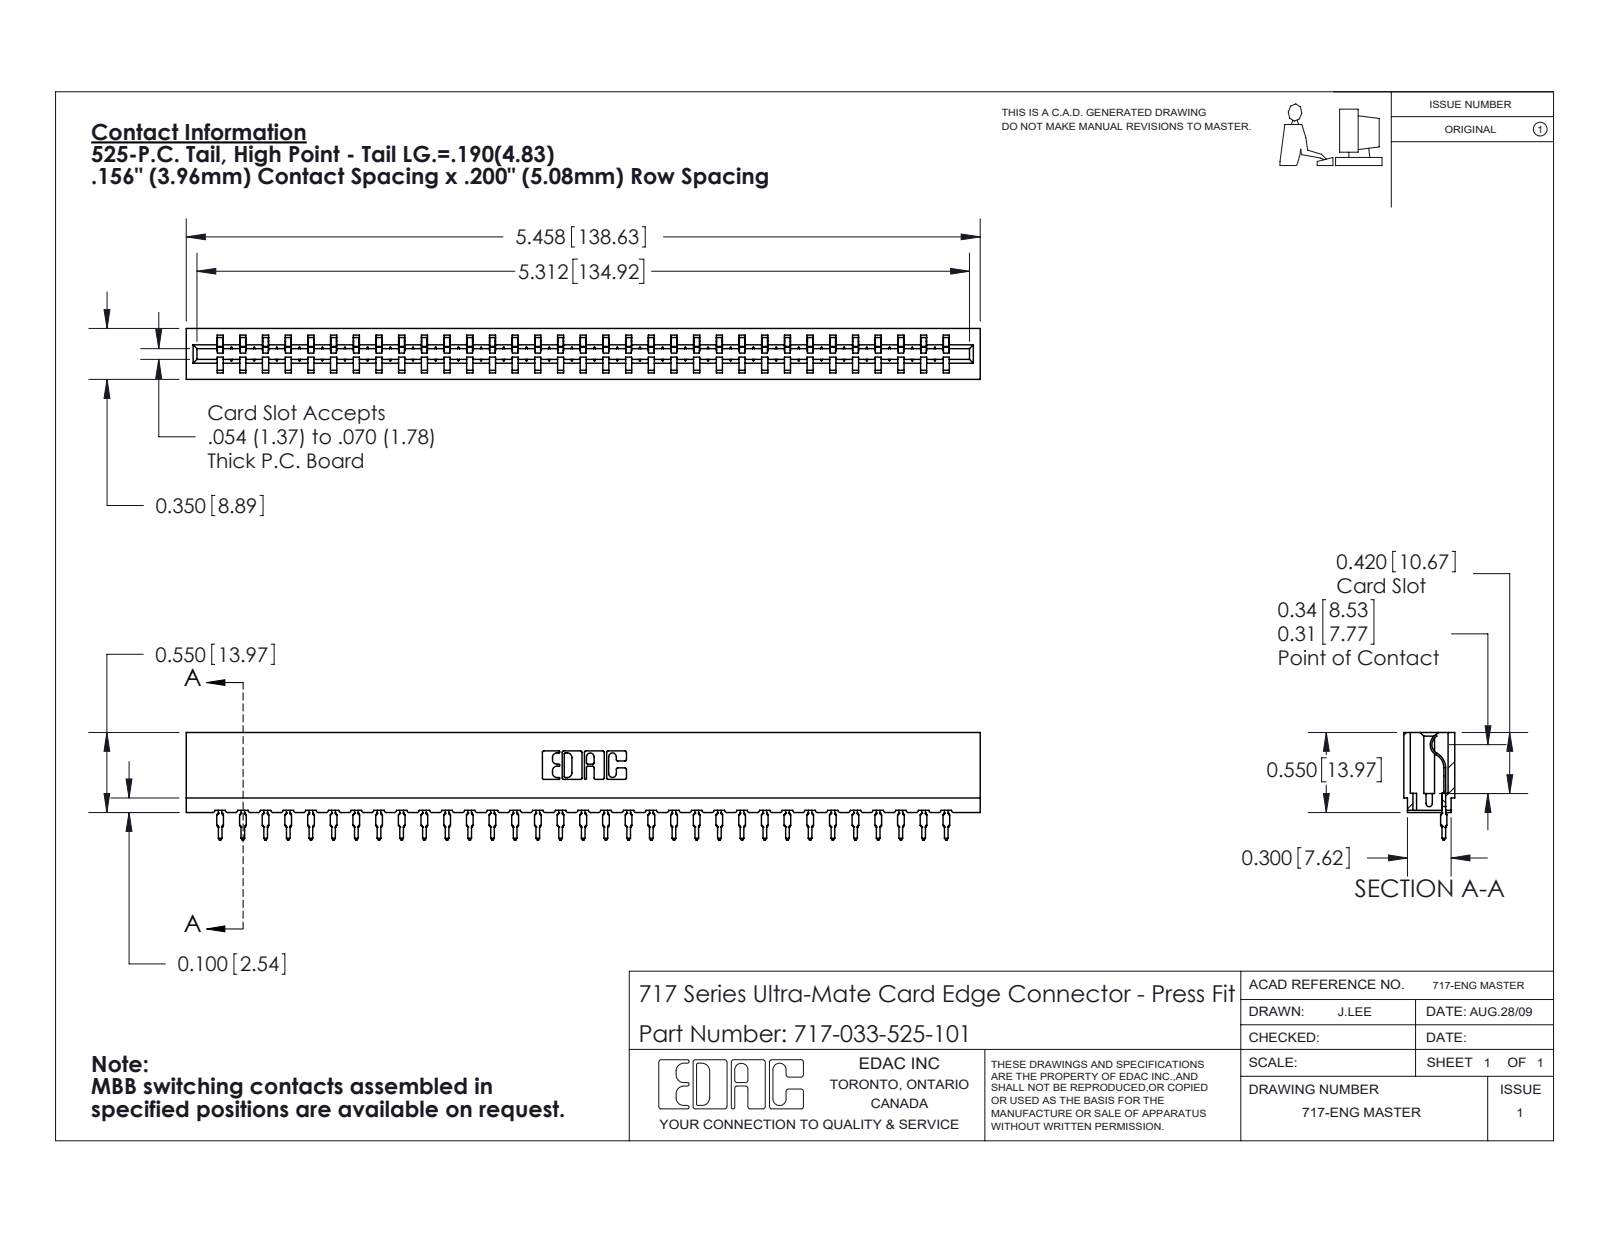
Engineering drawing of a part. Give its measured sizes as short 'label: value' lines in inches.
name: 745-292-001_525; 717-033-525-101; 717 Part_Insulator Option - 06
written by: SolidWorks 2020 (CONFIG_CONTROL_DESIGN)
unit: in
bodies: 34 solids, 3823 faces (2298 planar, 667 cylindrical, 858 other)
size: 5.458 × 0.739 × 0.35
volume: 0.715 in³; area: 25.21 in²
rounds: 66× R0.015, 66× R0.021, 22× R0.01, 6× R0.007, 6× R0.031, 4× R0.005, 4× R0.011, 3× R0.026
face distances: 0.212, 0.138, 0.35, 0.074, 0.045, 0.305, 0.093, 0.167, 0.025, 0.156
